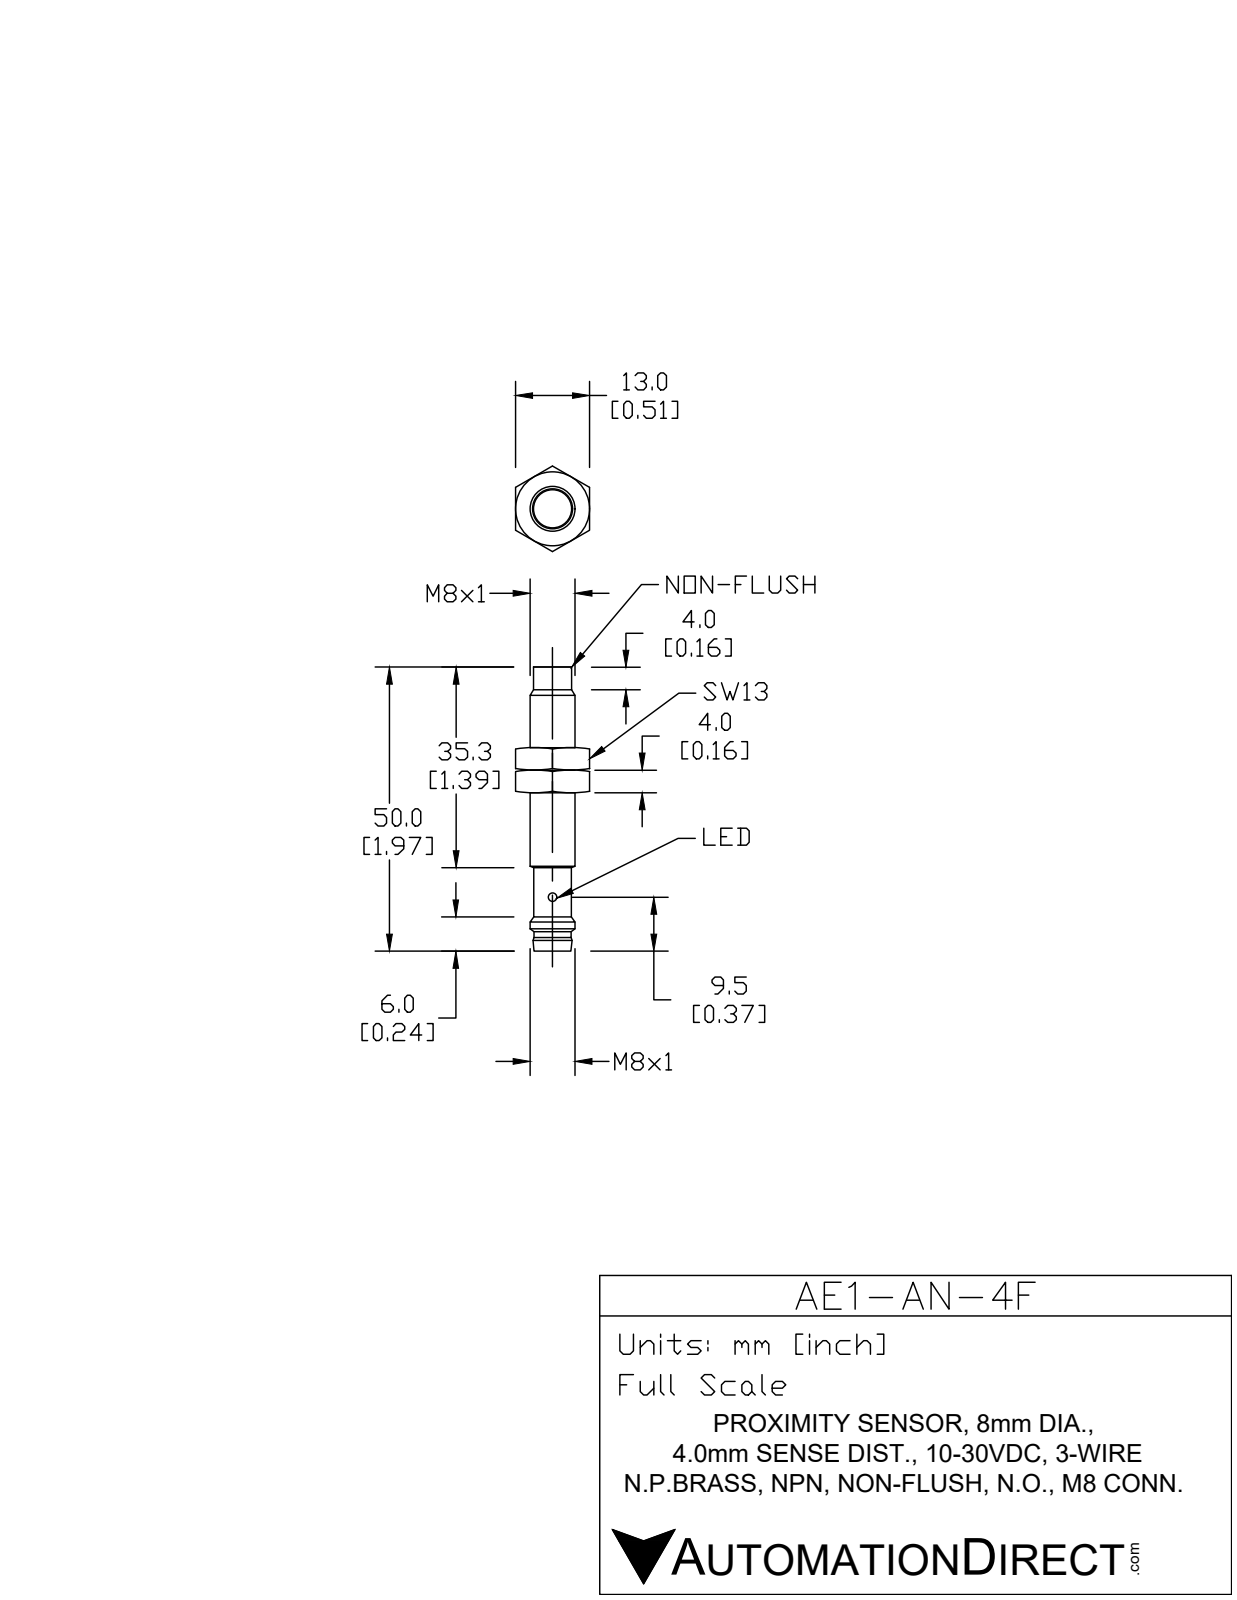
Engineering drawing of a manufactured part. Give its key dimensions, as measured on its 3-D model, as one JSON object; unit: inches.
{"part_name": "AE1-AN-4F", "step_written_by": "SolidWorks 2017 (AUTOMOTIVE_DESIGN)", "units": "inches", "bodies": {"solids": 3, "faces": 61, "planar": 11, "cylindrical": 30, "other": 20}, "overall_size": [1.976, 0.315, 0.315], "volume_in3": 0.139, "surface_area_in2": 2.574, "round_holes": [[0.079, 2], [0.228, 1]], "round_bosses_or_shafts": [[0.039, 3], [0.315, 1], [0.272, 1], [0.256, 1], [0.23, 1]], "face_to_face_distances": [1.622, 0.157, 1.78, 1.524, 1.366, 0.256, 1.976, 1.819, 0.453, 0.197]}
